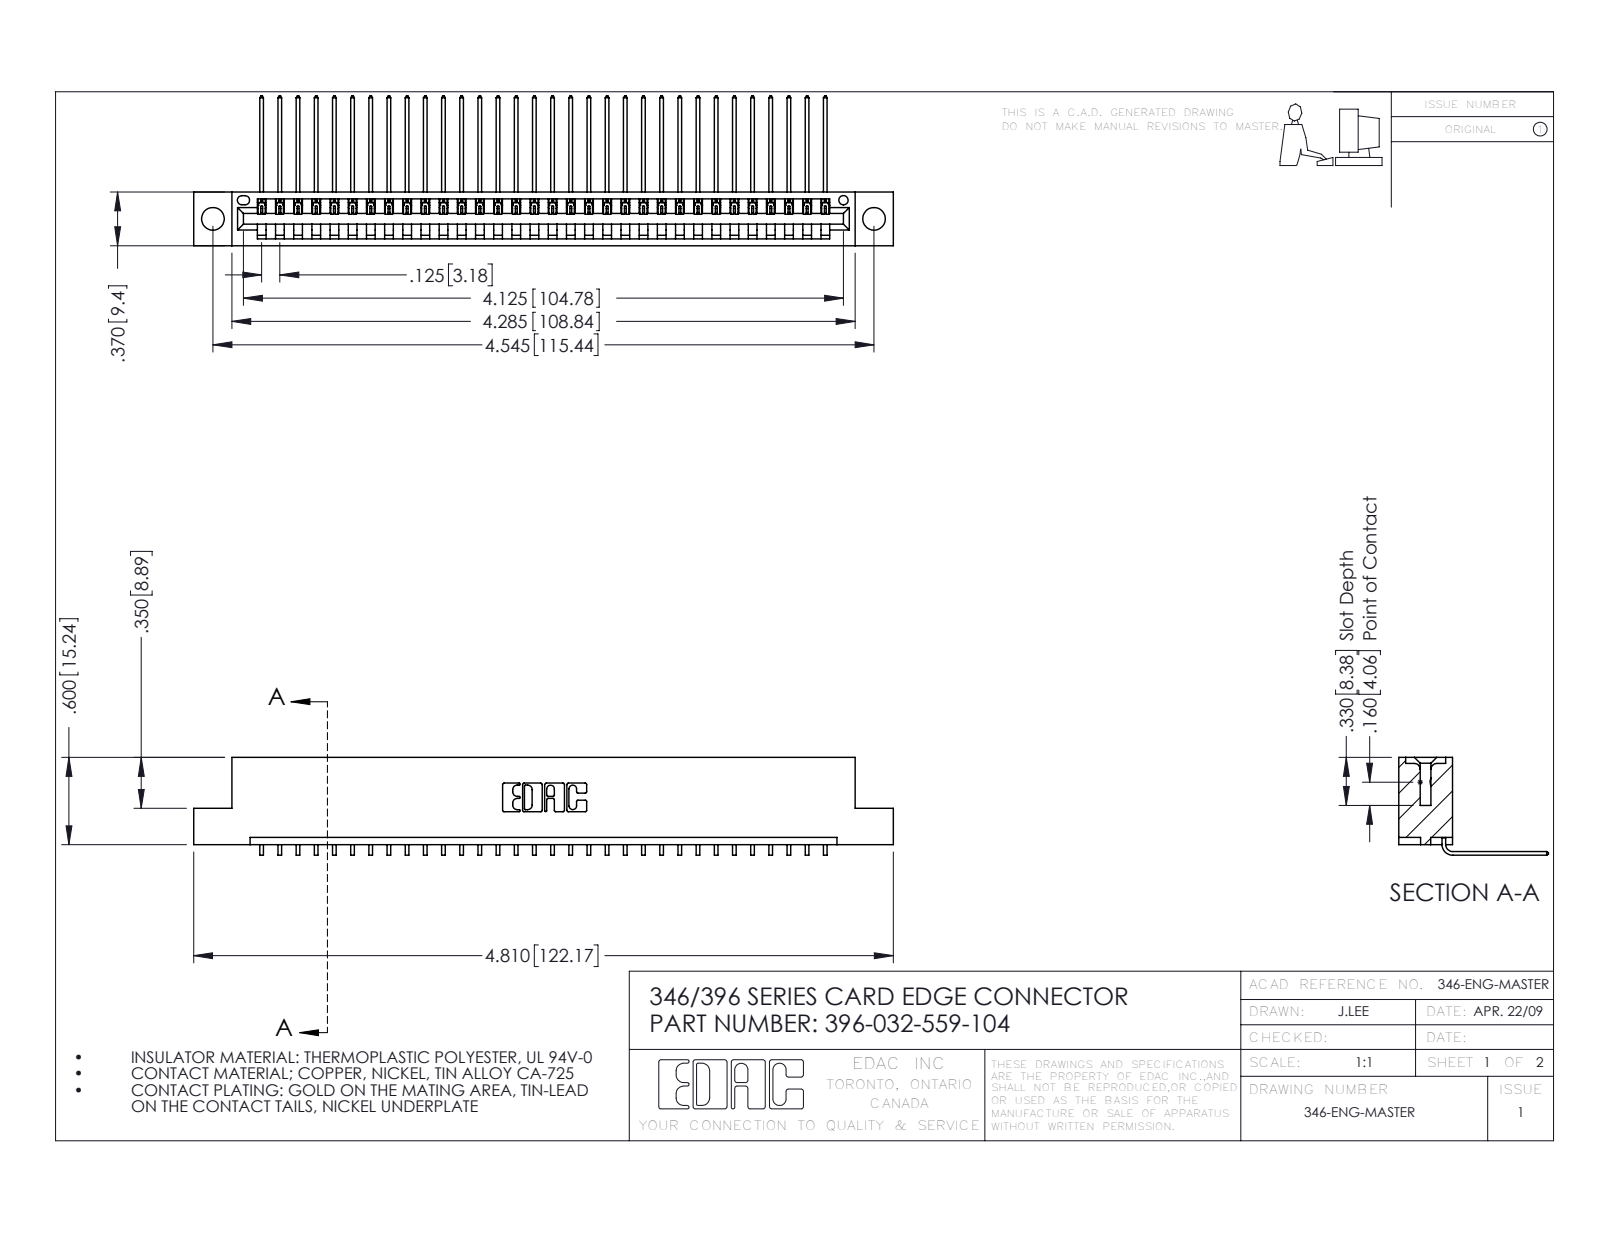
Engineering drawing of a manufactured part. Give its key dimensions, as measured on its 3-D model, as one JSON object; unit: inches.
{"part_name": "345-292-001_558 559 Tail - 1; 346 Part_Flush Mounting Lugs - 0.156 Dia-TH; 396-032-559-104", "step_written_by": "SolidWorks 2016 (CONFIG_CONTROL_DESIGN)", "units": "inches", "bodies": {"solids": 33, "faces": 2042, "planar": 1420, "cylindrical": 622, "other": 0}, "overall_size": [4.81, 1.03, 0.673], "volume_in3": 0.711, "surface_area_in2": 23.08, "round_holes": [[0.156, 2], [0.064, 1]], "partial_cylinders_radius": [[0.006, 64], [0.01, 22], [0.007, 6], [0.031, 6], [0.026, 3], [0.031, 2], [0.04, 2], [0.014, 1]], "face_to_face_distances": [0.048, 0.322, 0.37, 0.25, 0.072, 0.025, 0.298, 0.148, 0.222, 0.1], "hole_center_spacings": [0.246, 4.337, 4.545]}
